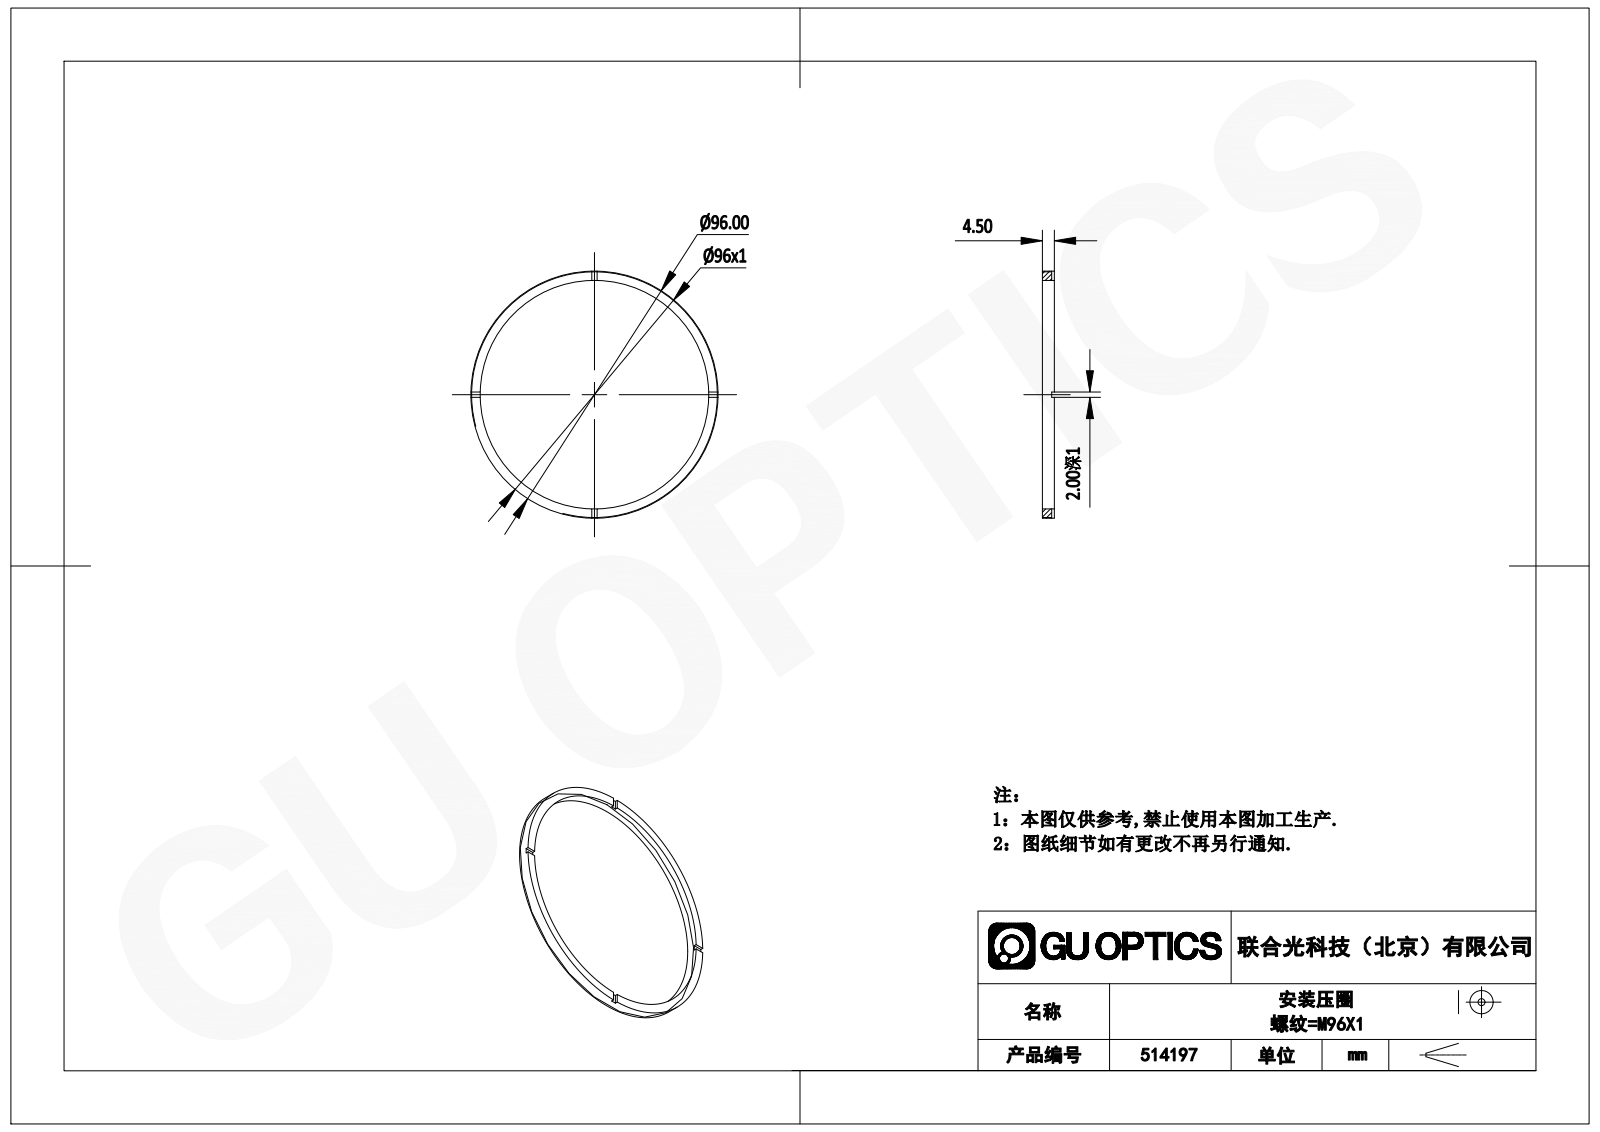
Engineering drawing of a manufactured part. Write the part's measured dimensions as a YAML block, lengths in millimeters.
part_name: "514197"
step_written_by: "SolidWorks 2020 (CONFIG_CONTROL_DESIGN)"
units: millimeters
bodies: {solids: 1, faces: 21, planar: 17, cylindrical: 4, other: 0}
overall_size: [96, 96, 4.5]
volume: 4549
surface_area: 4662
round_holes:
  - {diameter: 89, count: 1}
round_bosses_or_shafts:
  - {diameter: 96, count: 1}
face_to_face_distances: [4.5, 3.5, 1, 2]
